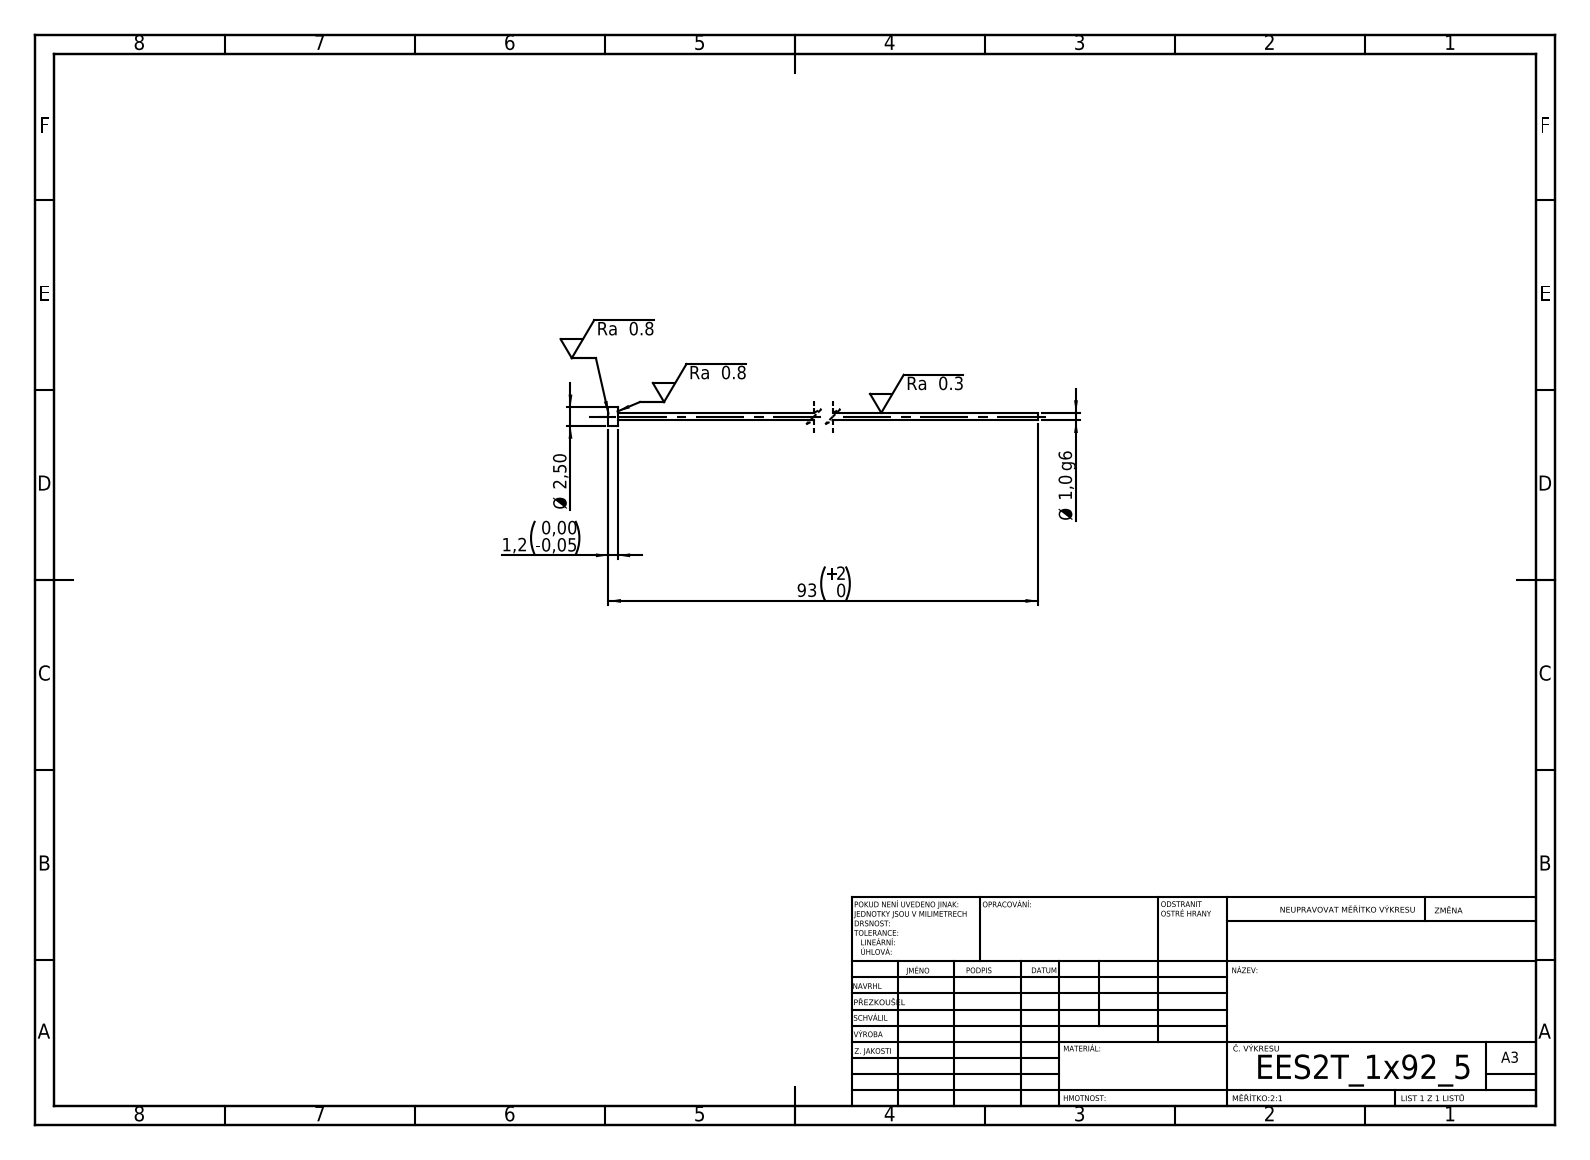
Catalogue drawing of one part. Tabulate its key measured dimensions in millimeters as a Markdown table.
| quantity | value |
| --- | --- |
| STEP written by | SolidWorks 2019 (CONFIG_CONTROL_DESIGN) |
| units | millimeters |
| bodies | 1 solid, 7 faces (3 planar, 4 cylindrical, 0 other) |
| overall size | 92.5 × 2.5 × 2.5 |
| volume | 78 mm³ |
| surface area | 306 mm² |
| round bosses / shafts (diameter × count) | 2.5 × 1, 1 × 1 |
| main face-to-face distances | 1.2, 92.5, 91.3 |
